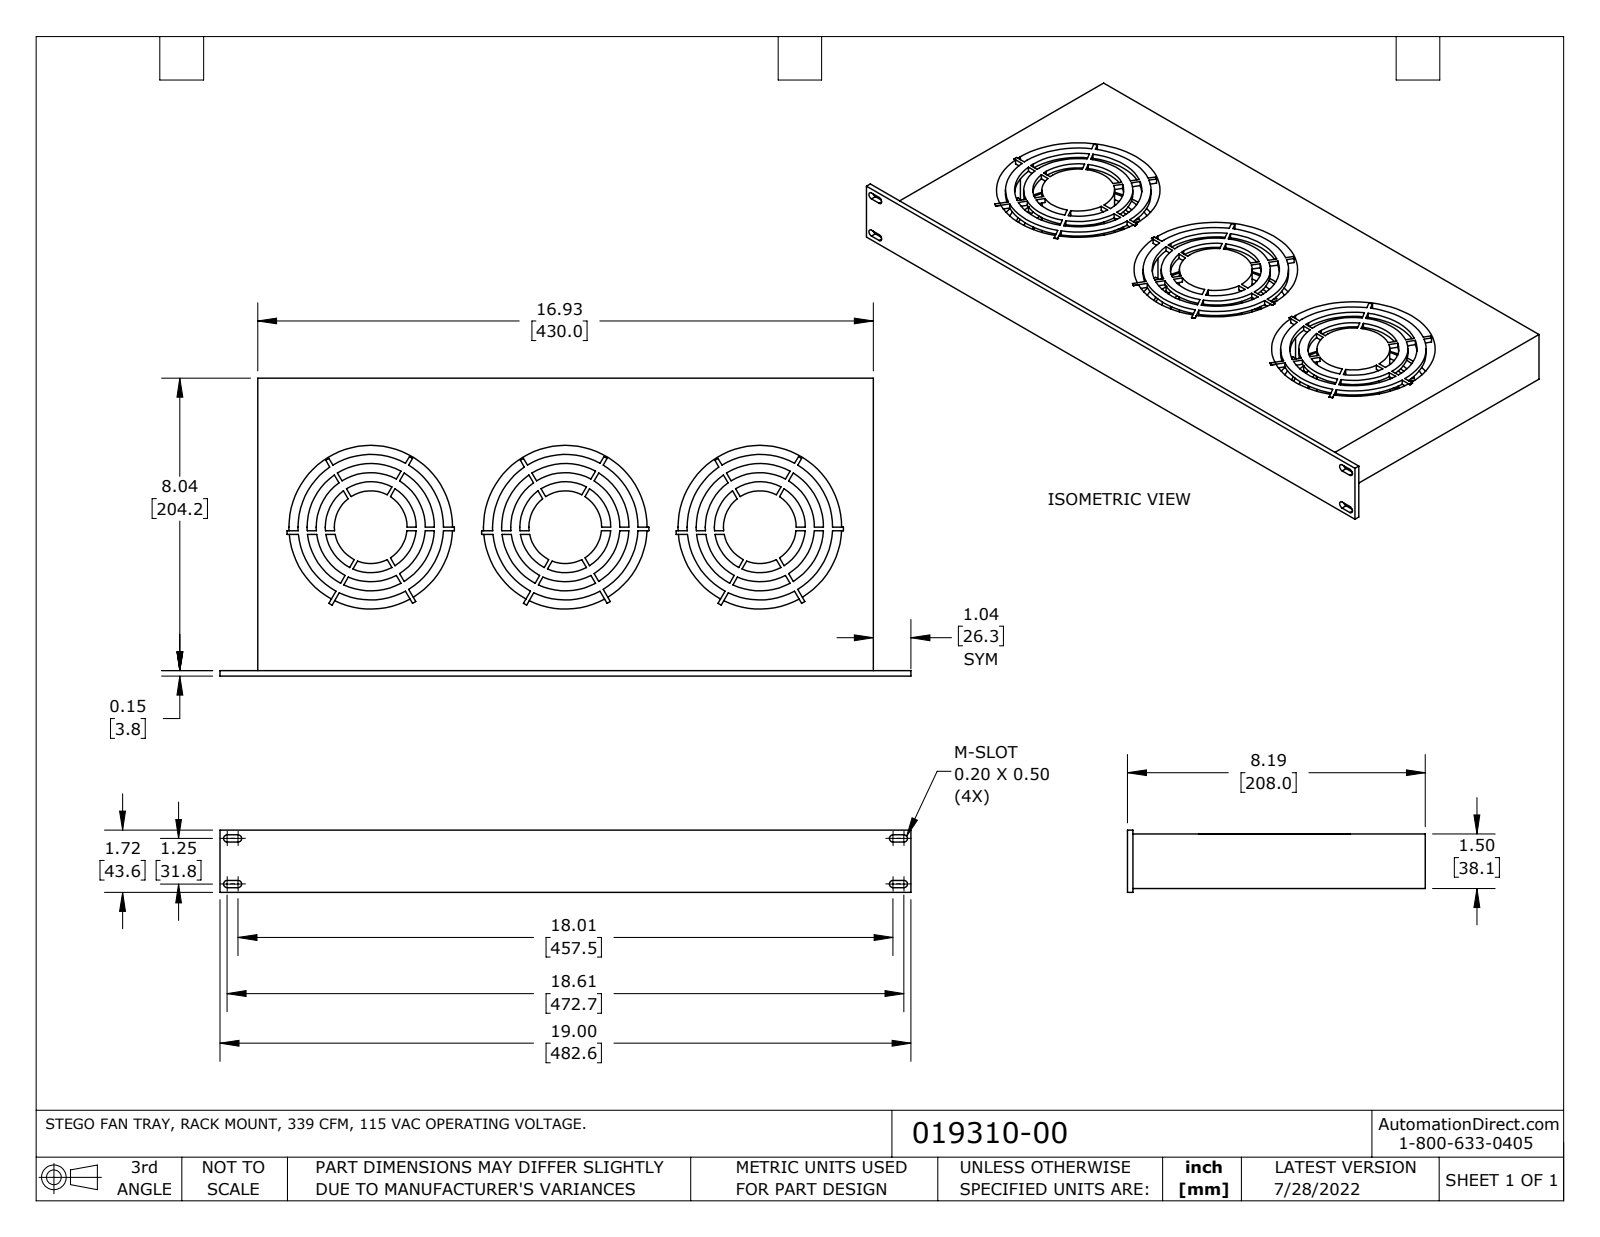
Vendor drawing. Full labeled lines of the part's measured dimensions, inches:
Part name (STEP PRODUCT): 019310-00_Default
STEP written by: SolidWorks 2021 (CONFIG_CONTROL_DESIGN)
Units: inches
Bodies: 1 solid, 504 faces (316 planar, 188 cylindrical, 0 other)
Overall size (bounding box): 19 × 8.189 × 1.717
Volume: 156.6 in³ · Surface area: 534.7 in²
Round holes (diameter × count): ⌀2.5 ×3, ⌀3.5 ×3, ⌀4.5 ×3
Round bosses / shafts (diameter × count): ⌀4 ×3, ⌀3 ×3, ⌀2 ×3
Partial cylindrical surfaces — rounded edges, fillets, slot ends (radius × count): R0.1 ×8
Main face-to-face distances: 1.5, 1.502, 8.189, 1.498, 1.364, 1.362, 0.136, 0.138, 0.164, 0.162
Hole centre spacings: 5.35, 10.7
